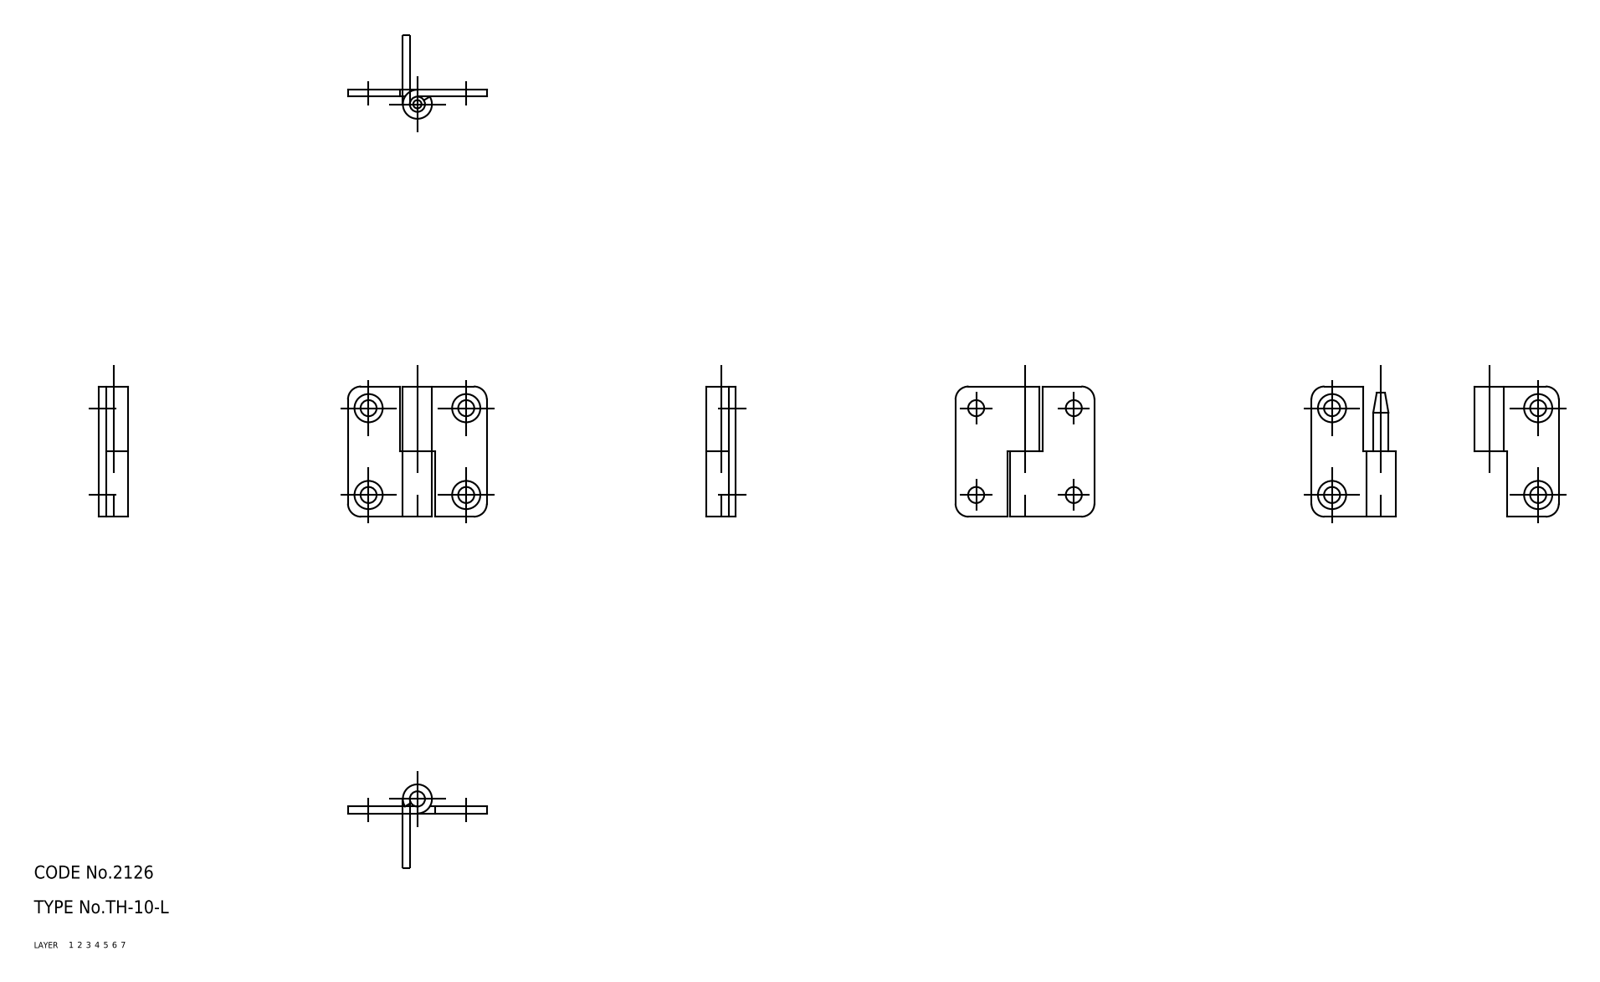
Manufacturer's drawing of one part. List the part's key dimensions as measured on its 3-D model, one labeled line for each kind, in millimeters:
Part name (STEP PRODUCT): shaft; hinge piece_B; hinge piece_A; TH_10_L_31818_36
STEP written by: CADfix (AUTOMOTIVE_DESIGN)
Units: millimetres
Bodies: 3 solids, 46 faces (0 planar, 0 cylindrical, 46 other)
Overall size (bounding box): 32 × 30 × 6.7
Volume: 2 106 mm³ · Surface area: 3 115 mm²
